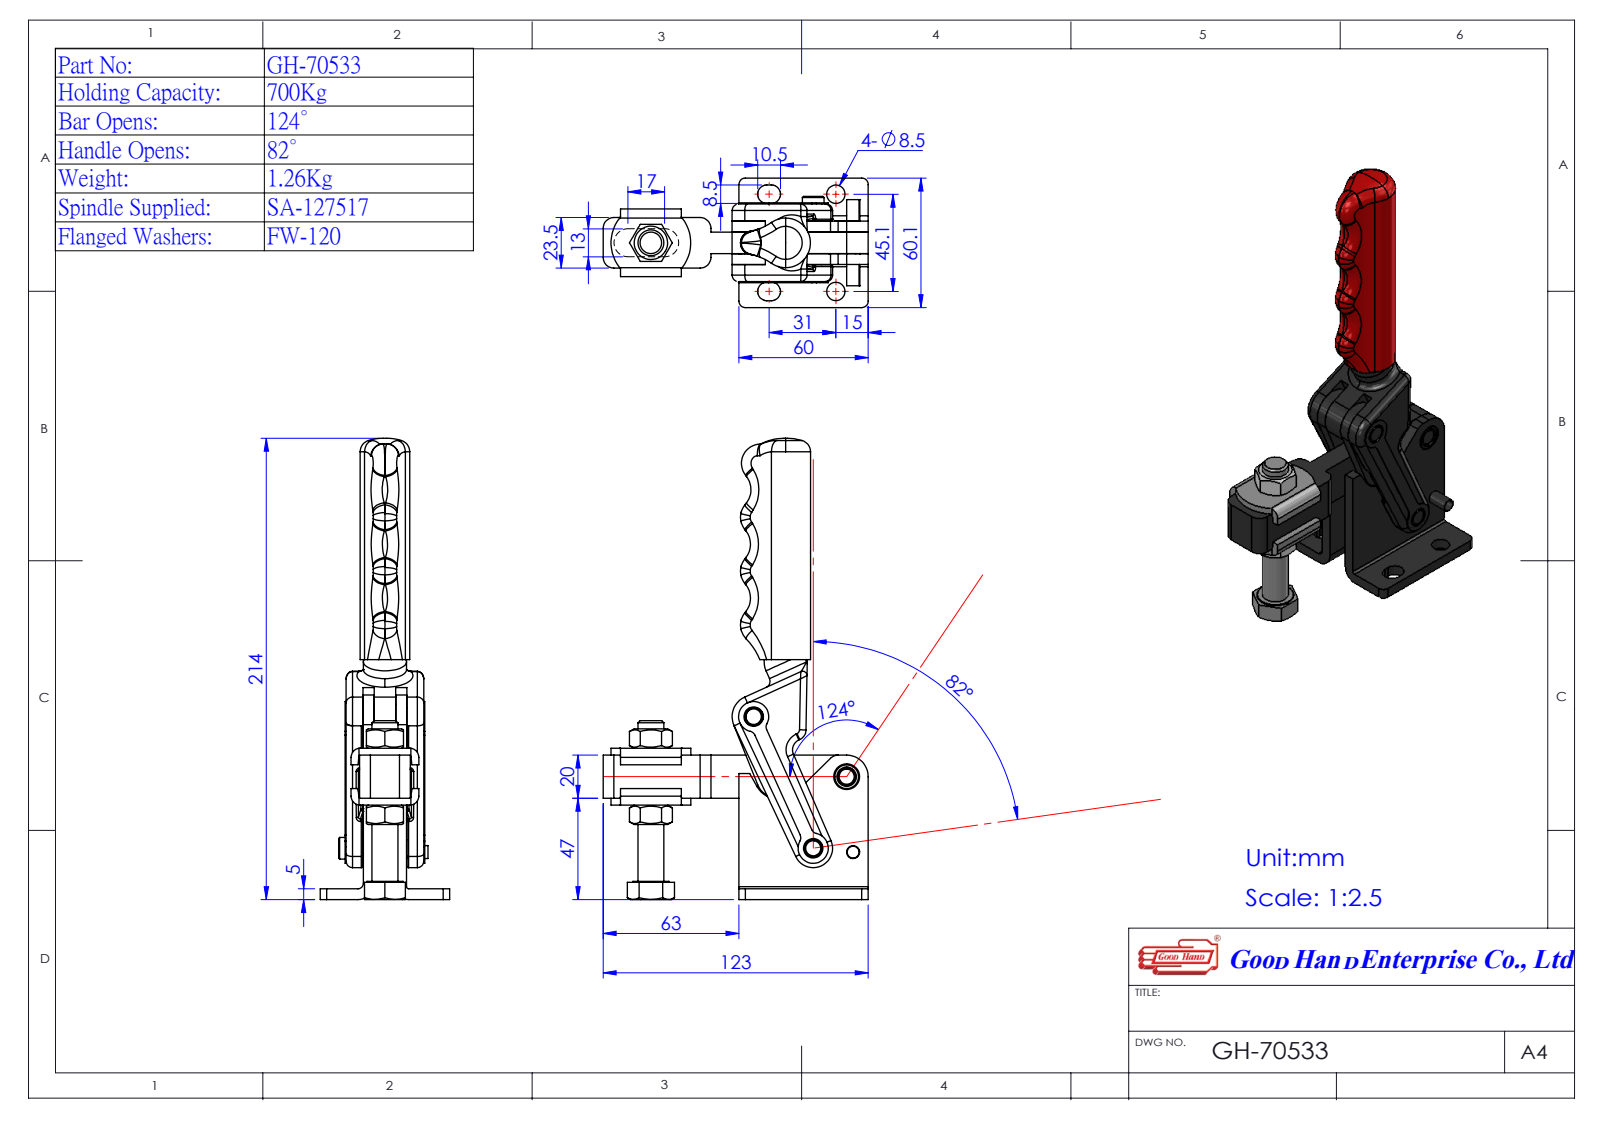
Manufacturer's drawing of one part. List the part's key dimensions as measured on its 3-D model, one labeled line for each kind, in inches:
Part name (STEP PRODUCT): GH-SA-127517-1^GH-70533(簡化); 70533-BAR-47053308-a-1^GH-70533(簡化); Group5^GH-70533(簡化); Group1^GH-70533(簡化) (+3 more)
STEP written by: SolidWorks 2016 (AUTOMOTIVE_DESIGN)
Units: inches
Bodies: 7 solids, 388 faces (143 planar, 157 cylindrical, 88 other)
Overall size (bounding box): 8.663 × 4.843 × 2.366
Volume: 12.51 in³ · Surface area: 110.7 in²
Round holes (diameter × count): ⌀0.236 ×4, ⌀0.335 ×2, ⌀0.217 ×1, ⌀0.472 ×1, ⌀0.512 ×1
Round bosses / shafts (diameter × count): ⌀0.236 ×3, ⌀0.551 ×2, ⌀0.787 ×1, ⌀0.752 ×1, ⌀0.669 ×1, ⌀0.472 ×1, ⌀0.394 ×1, ⌀0.322 ×1
Partial cylindrical surfaces — rounded edges, fillets, slot ends (radius × count): R0.118 ×18, R0.197 ×10, R0.787 ×7, R0.039 ×5, R0.394 ×5, R0.165 ×4, R0.169 ×4, R0.276 ×4
Main face-to-face distances: 0.197, 0.594, 0.596, 0.199, 0.593, 0.396, 0.787, 0.201, 0.203, 0.598
Hole centre spacings: 3.54, 0.713, 1.181, 1.26, 1.47, 1.514, 1.53, 1.776
